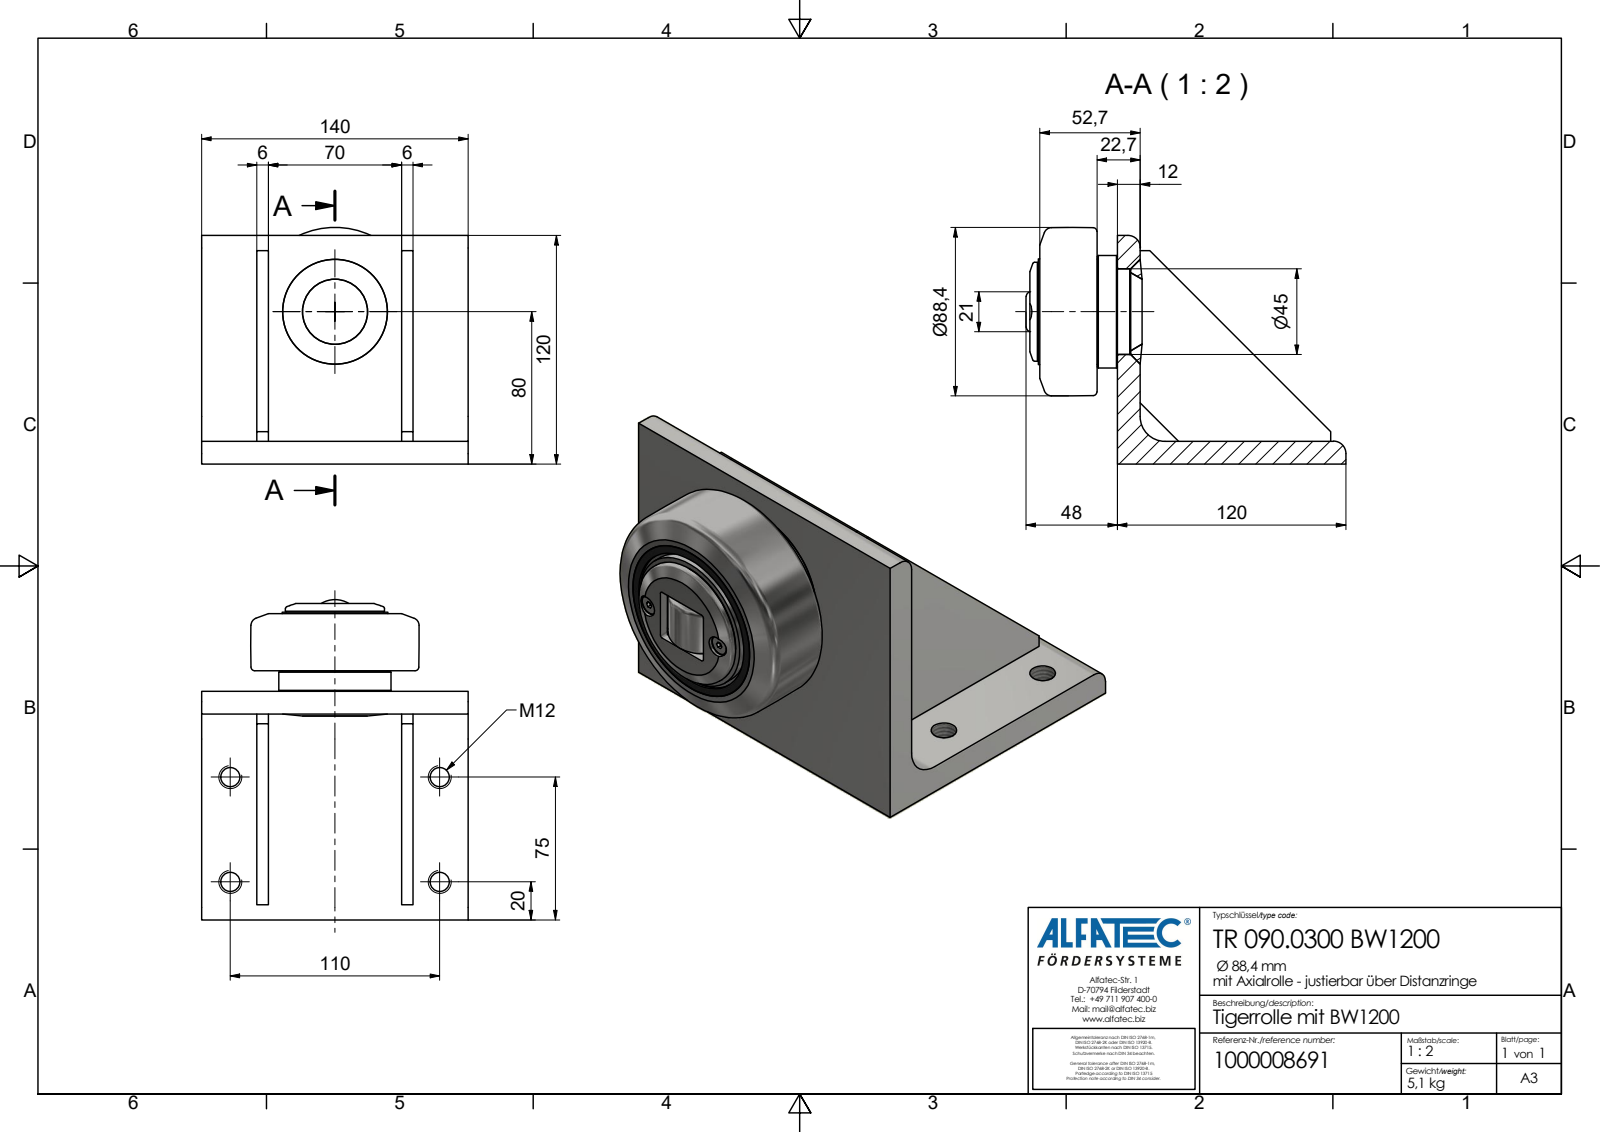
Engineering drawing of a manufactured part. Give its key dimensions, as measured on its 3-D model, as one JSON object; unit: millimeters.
{"part_name": "TR 090.0300 BW1200_Kontur", "step_written_by": "Autodesk Inventor 2020 (AP242_MANAGED_MODEL_BASED_3D_ENGINEERING_MIM_LF)", "units": "millimeters", "bodies": {"solids": 1, "faces": 97, "planar": 57, "cylindrical": 25, "other": 15}, "overall_size": [168, 140, 124.2], "volume_mm3": 665429, "surface_area_mm2": 111532, "round_holes": [[10.11, 4], [8.6, 2]], "round_bosses_or_shafts": [[7.8, 2], [59, 1], [55.5, 1], [55.3, 1], [52, 1]], "partial_cylinders_radius": [[1, 4], [6.5, 2], [8, 1], [9, 1], [10.5, 1], [13, 1]], "face_to_face_distances": [12, 76, 6, 29, 35, 105, 111, 82, 70, 10.7], "hole_center_spacings": [55, 110, 122.98, 39]}
